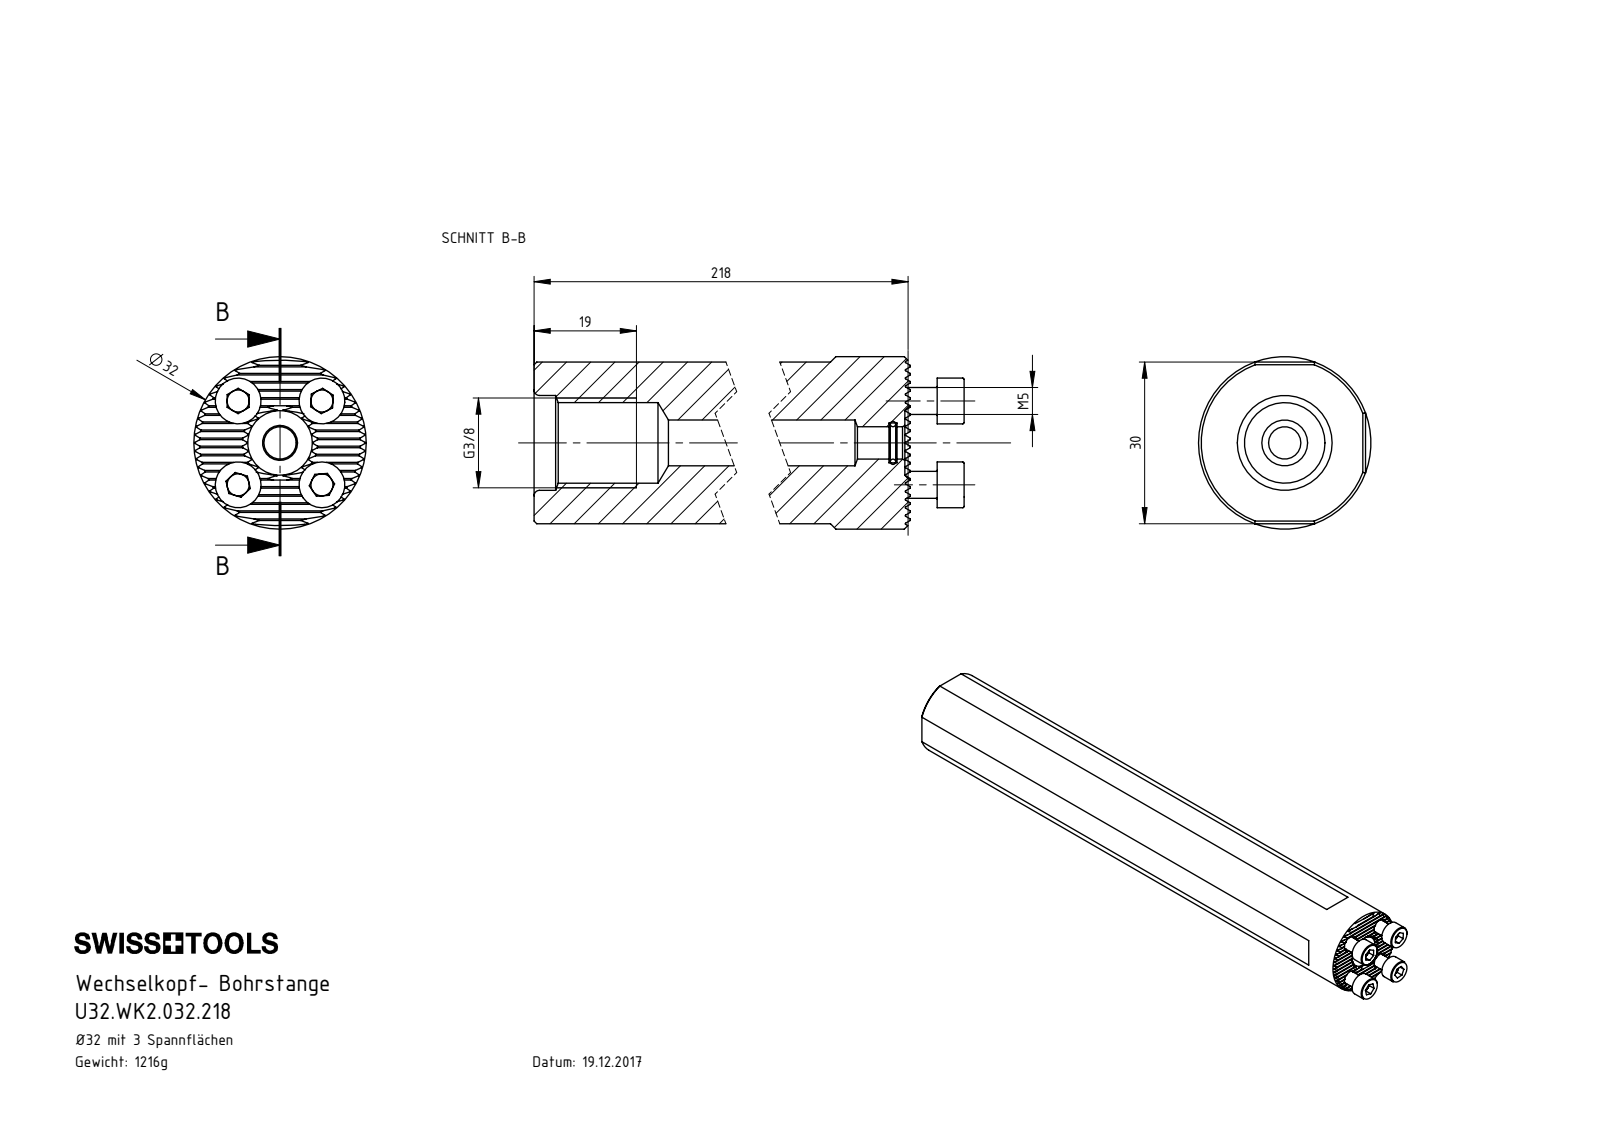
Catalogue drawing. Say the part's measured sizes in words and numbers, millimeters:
The part is named "U32.WK2.032.218; U32-WK2.032.218_A; DIN 3771 - 6x1; ISO 4762 - M5 x 14". Its 3-D file was written by "SolidWorks 2017 (AUTOMOTIVE_DESIGN)". It is 5 solids with 326 faces: 188 planar, 76 cylindrical and 62 other. Overall it measures 228.4 by 32 by 32 millimeters. Its volume is 156 163 cubic millimeters and its surface area 32 034 square millimeters. Round holes: 4 of diameter 4.2, 1 of diameter 6, 1 of diameter 7.4, 1 of diameter 8.5, 1 of diameter 14.95, 1 of diameter 17.6. Round bosses or shafts: 3 of diameter 8.5, 3 of diameter 5, 1 of diameter 32. Partial cylindrical surfaces (rounded edges, fillets, slot ends): 21 of radius 0.12. The main face-to-face distances are 30, 1.3, 2.6, 3.9, 5.2, 12.99, 6.5, 11.69, 14.29, 10.39. The hole center spacings are 11, 15.56, 22.01.
